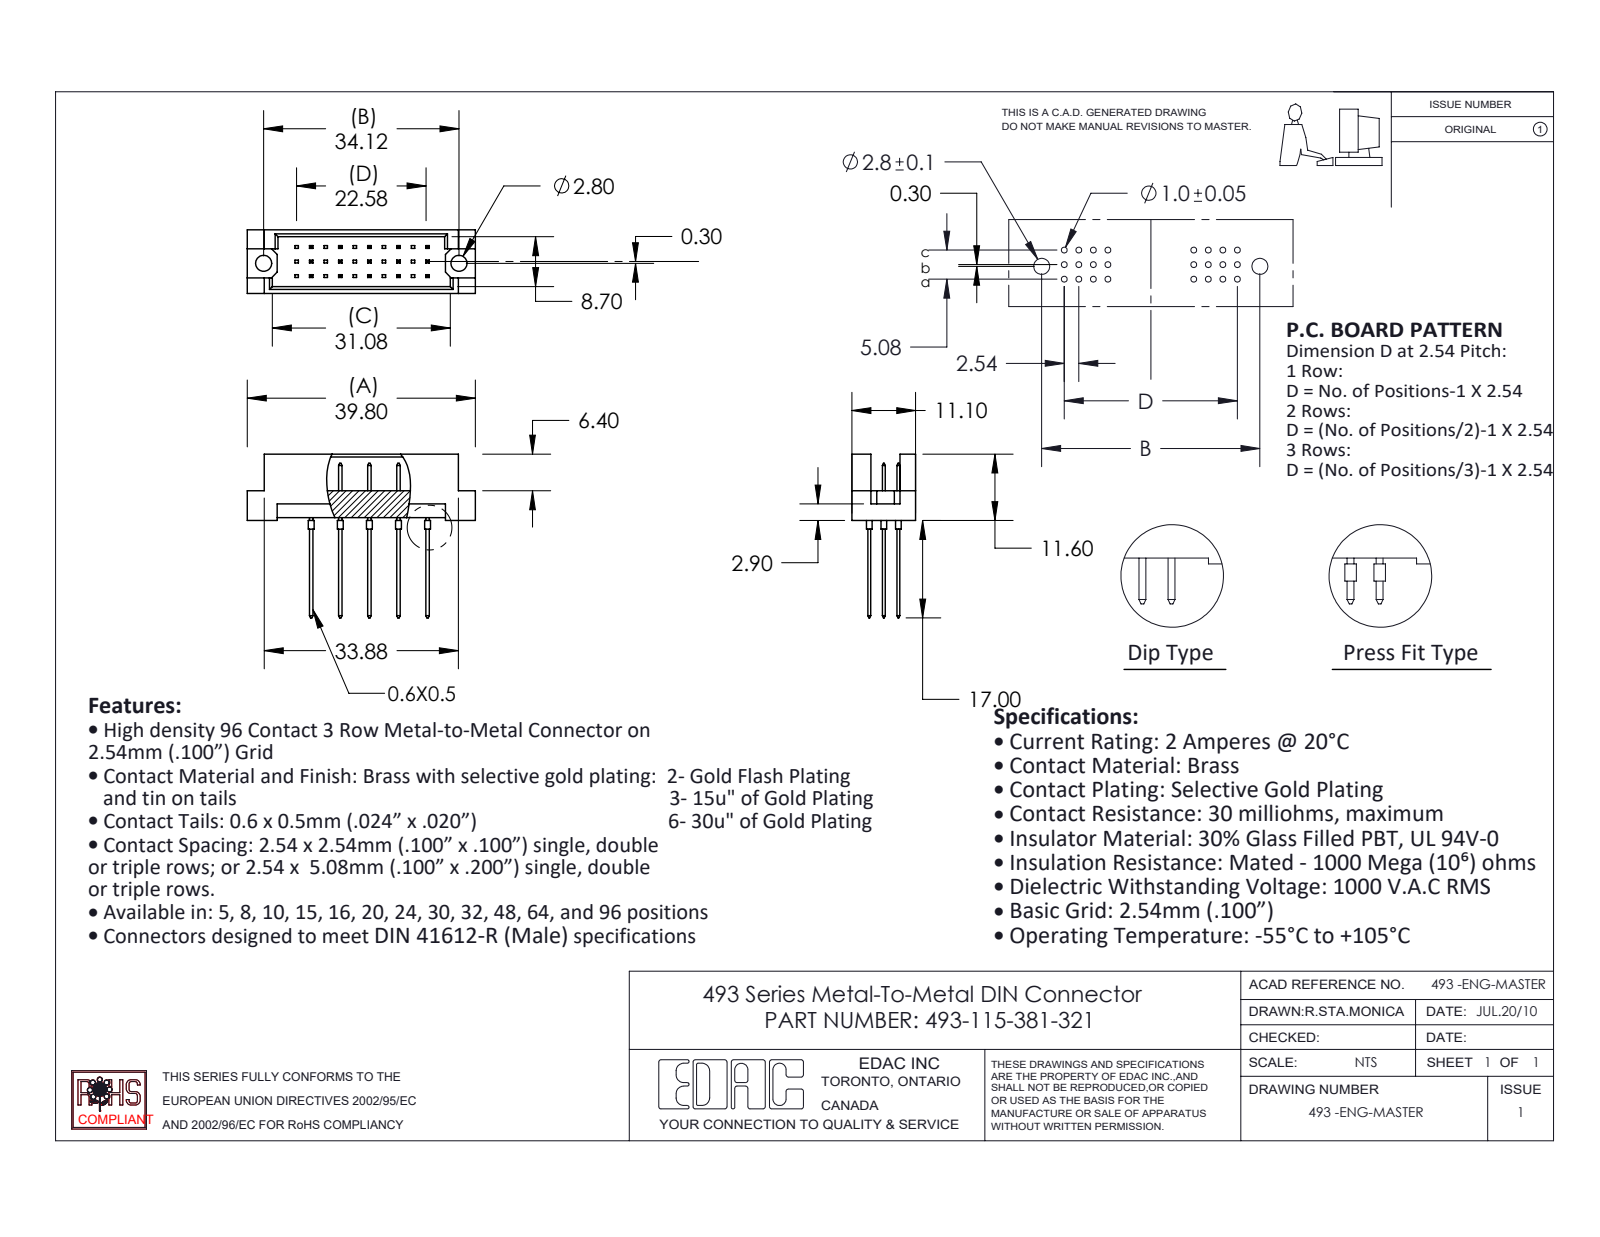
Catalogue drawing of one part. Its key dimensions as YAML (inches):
part_name: "493-290_81; 493 Part_30; 493-115-381-321"
step_written_by: "SolidWorks 2020 (CONFIG_CONTROL_DESIGN)"
units: inches
bodies: {solids: 16, faces: 502, planar: 468, cylindrical: 34, other: 0}
overall_size: [1.567, 1.126, 0.437]
volume: 0.153
surface_area: 5.671
round_holes:
  - {diameter: 0.11, count: 2}
round_bosses_or_shafts:
  - {diameter: 0.039, count: 15}
face_to_face_distances: [0.2, 0.047, 0.39, 0.02, 0.1, 0.437, 0.343, 0.4, 0.185, 0.024]
hole_center_spacings: [1.343]
